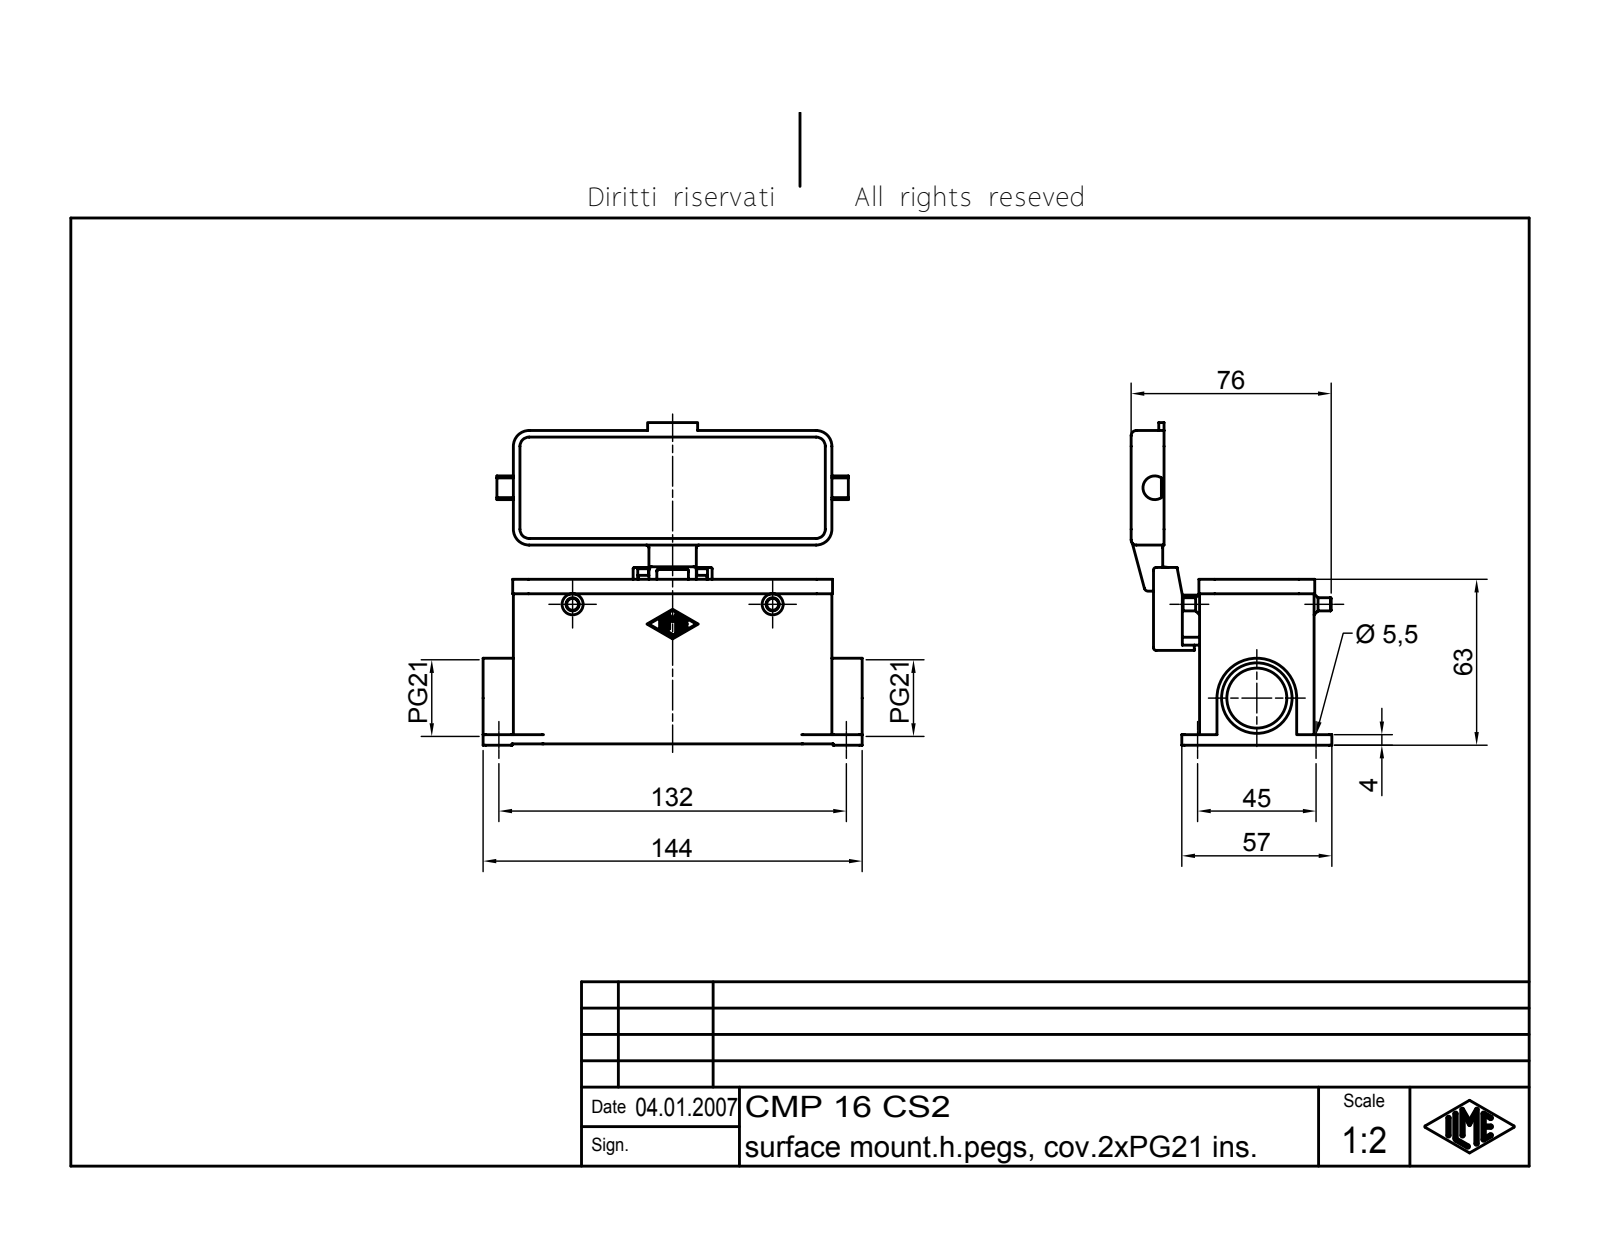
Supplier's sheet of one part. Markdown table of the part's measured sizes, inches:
| quantity | value |
| --- | --- |
| part name | CMP 16 CS2 |
| STEP written by | Autodesk Inventor 7 (AUTOMOTIVE_DESIGN) |
| units | inches |
| bodies | 2 solids, 474 faces (177 planar, 177 cylindrical, 120 other) |
| overall size | 5.669 × 4.823 × 3.002 |
| volume | 8.221 in³ |
| surface area | 121.3 in² |
| round holes (diameter × count) | 0.217 × 4, 0.157 × 1, 0.197 × 1, 0.897 × 1, 1.054 × 1 |
| round bosses / shafts (diameter × count) | 0.197 × 2, 0.118 × 2, 0.276 × 1, 0.157 × 1 |
| partial cylindrical surfaces (radius × count) | 0.039 × 26, 0.015 × 14, 0.236 × 12, 0.02 × 9, 0.028 × 8, 0.079 × 8, 0.118 × 4, 0.138 × 4 |
| main face-to-face distances | 0.118, 1.594, 0.138, 1.713, 1.476, 2.48, 2.736, 2.618, 0.886, 1.142 |
| hole center spacings | 1.772, 5.197, 5.491 |
